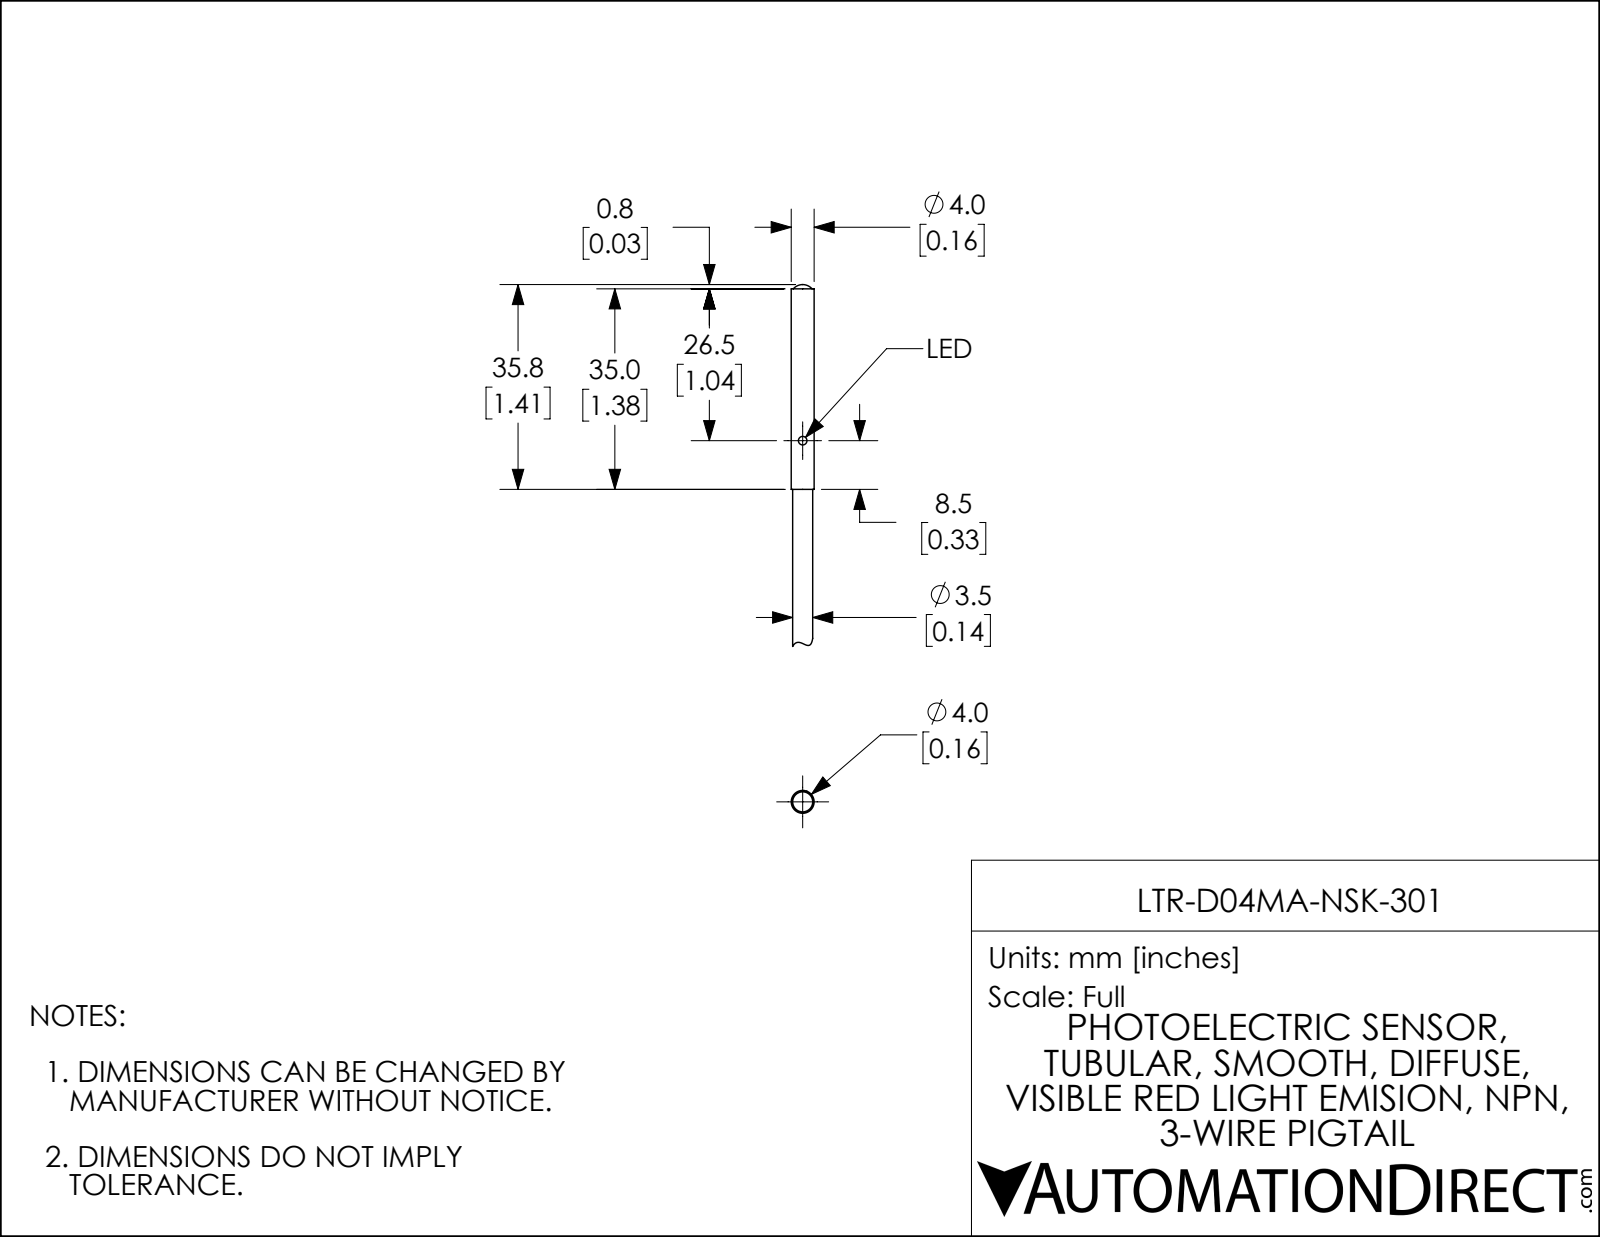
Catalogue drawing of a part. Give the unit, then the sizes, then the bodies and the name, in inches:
Units: inches
Overall size (bounding box): 2.487 × 0.157 × 0.157
Round holes (diameter × count): ⌀0.059 ×1, ⌀0.14 ×1
Round bosses / shafts (diameter × count): ⌀0.157 ×1, ⌀0.138 ×1, ⌀0.136 ×1
Main face-to-face distances: 1.378, 0.016, 1.362
Volume: 0.043 in³ · Surface area: 1.199 in²
Bodies: 1 solid, 11 faces (3 planar, 6 cylindrical, 2 other)
Part name (STEP PRODUCT): LxR-D04MA-Nxx
STEP written by: SolidWorks 2018 (AUTOMOTIVE_DESIGN)
